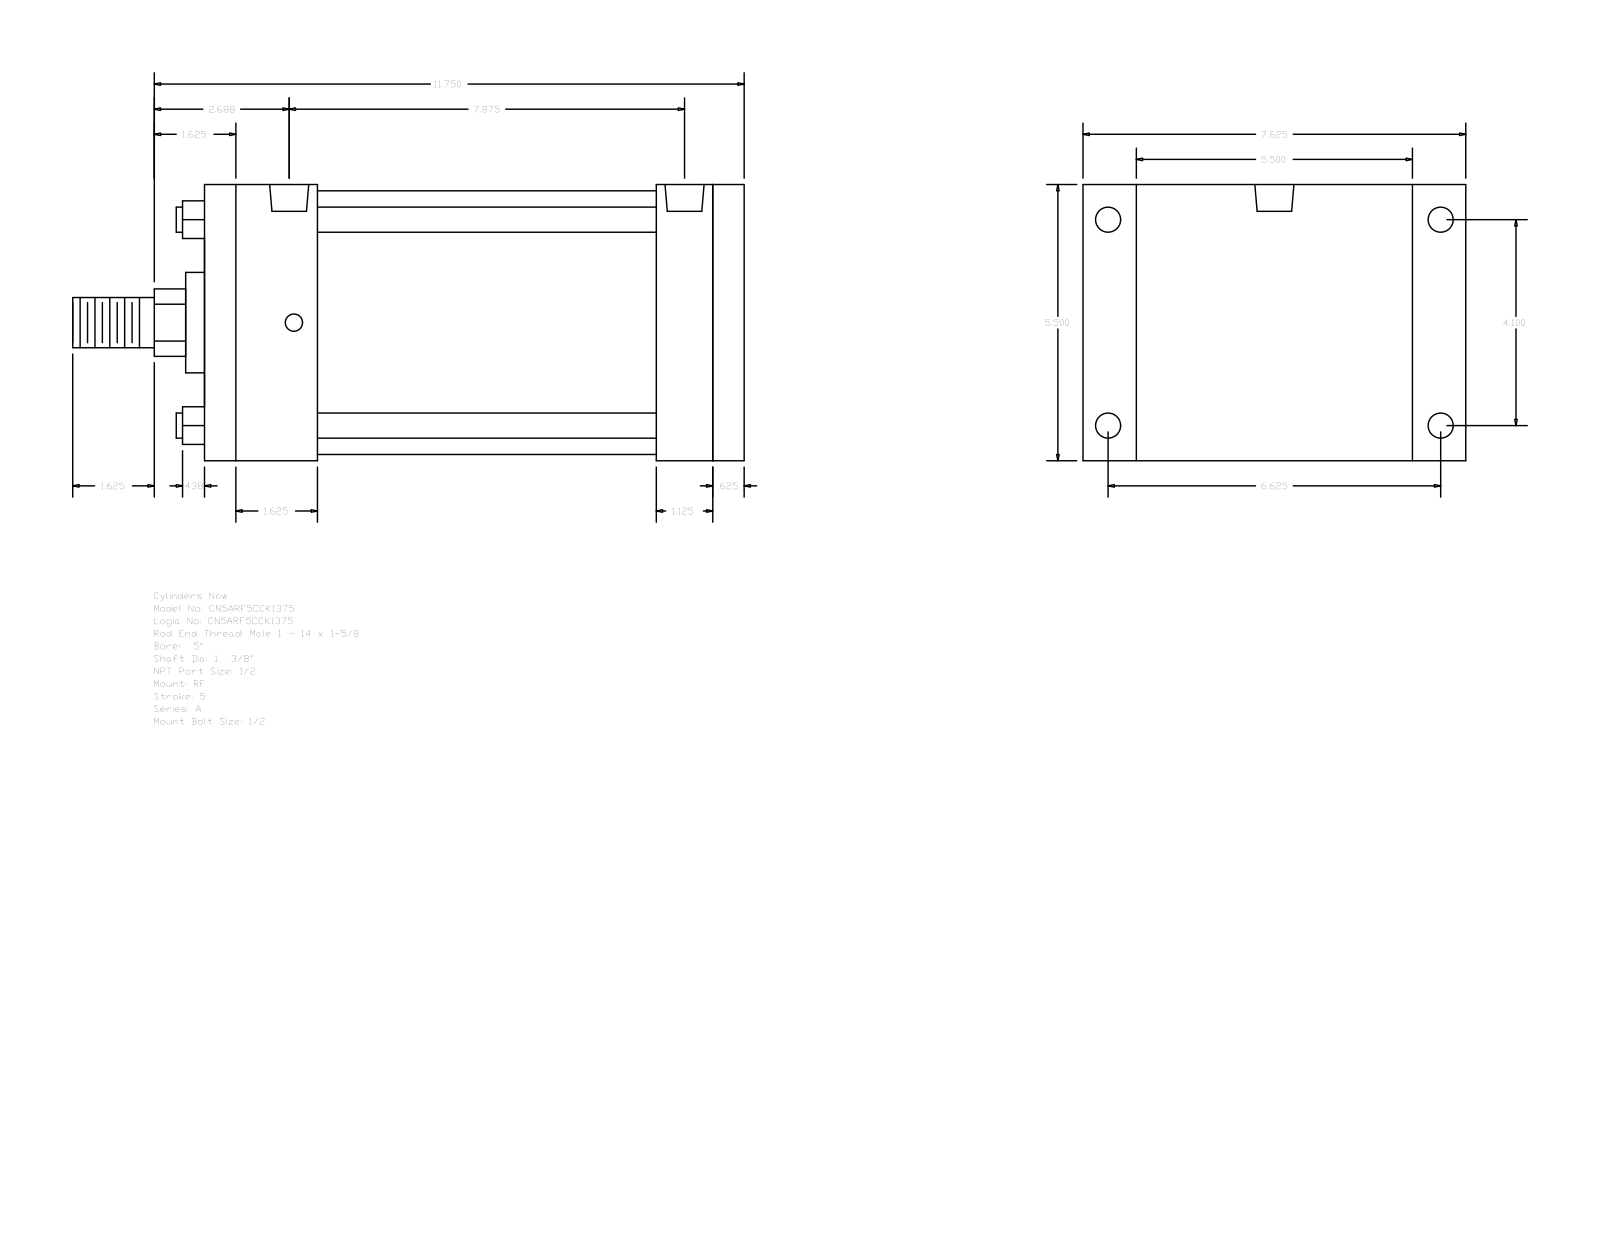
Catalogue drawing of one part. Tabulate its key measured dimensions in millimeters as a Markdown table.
| quantity | value |
| --- | --- |
| part name | A_RF__0500_1.375 |
| STEP written by | GSSL Pune (CONFIG_CONTROL_DESIGN) |
| units | millimeters |
| bodies | 0 solids, 92 faces (64 planar, 28 cylindrical, 0 other) |
| overall size | 339.73 × 193.68 × 139.7 |
| round holes (diameter × count) | 8.73 × 4, 12.7 × 4, 19.77 × 2 |
| round bosses / shafts (diameter × count) | 12.7 × 4, 133.35 × 1, 50.8 × 1, 34.92 × 1, 25.4 × 1 |
| partial cylindrical surfaces (radius × count) | 17.06 × 1 |
| main face-to-face distances | 139.7, 273.05, 15.88, 257.17, 57.15, 200.02, 215.9, 228.6, 171.45, 28.57 |
| hole center spacings | 2.39, 104.14, 168.28, 195.25, 197.64, 197.9, 200.03 |
